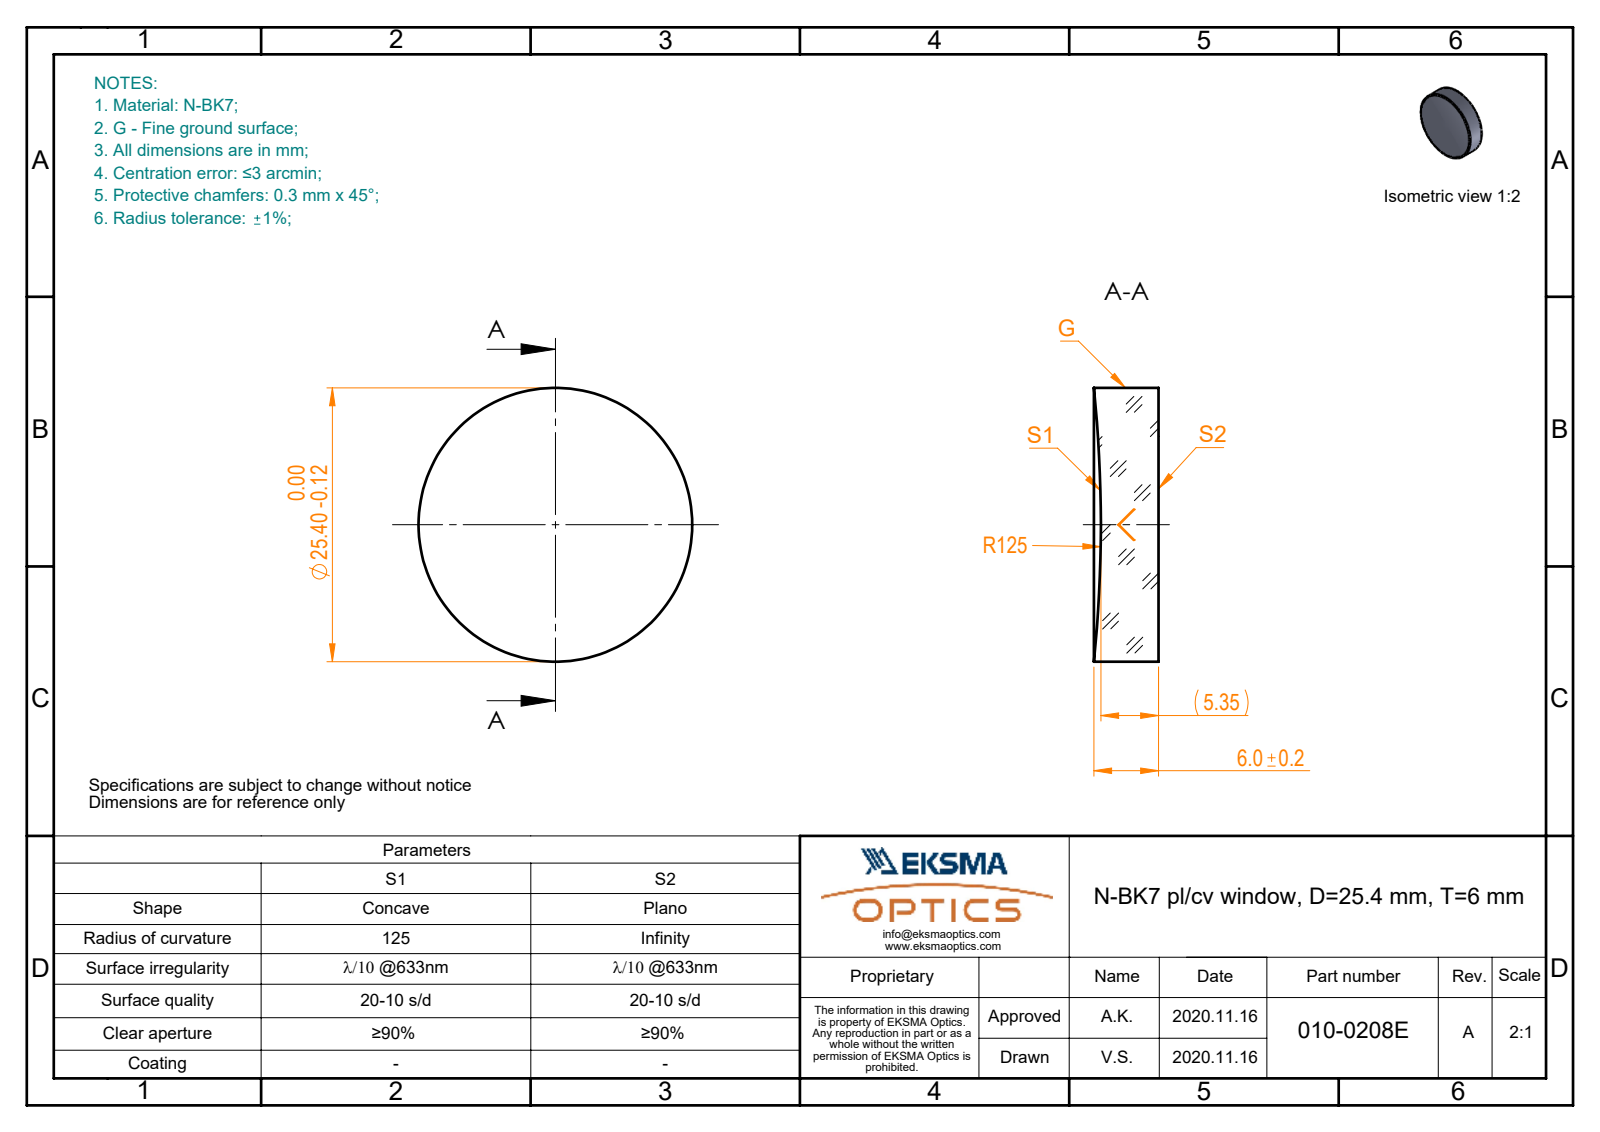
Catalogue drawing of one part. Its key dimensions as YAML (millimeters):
part_name: "010-0208E_N-BK7_PCV_window"
step_written_by: "SolidWorks 2019 (CONFIG_CONTROL_DESIGN)"
units: millimeters
bodies: {solids: 1, faces: 5, planar: 1, cylindrical: 2, other: 2}
overall_size: [25.4, 25.4, 6]
volume: 2876
surface_area: 1494
round_bosses_or_shafts:
  - {diameter: 25.4, count: 1}
